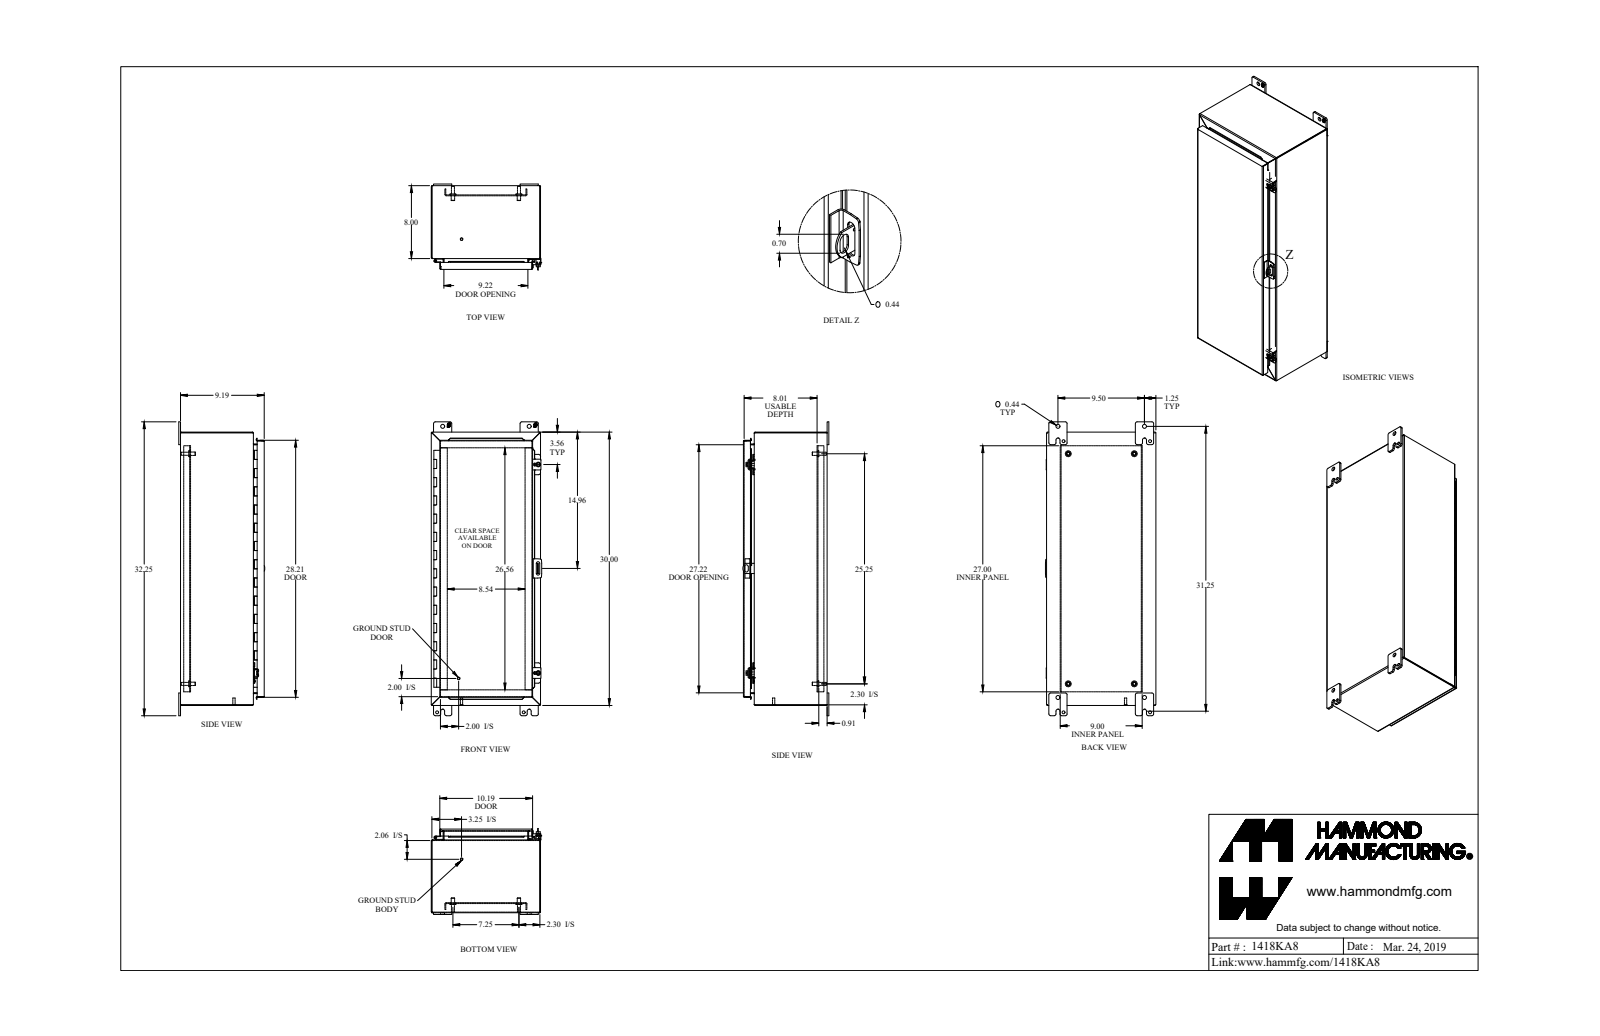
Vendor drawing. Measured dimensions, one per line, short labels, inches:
name: 1418KA8_Default
written by: SolidWorks 2019 (CONFIG_CONTROL_DESIGN)
unit: in
bodies: 38 solids, 1209 faces (739 planar, 402 cylindrical, 68 other)
size: 32.25 × 12.125 × 9.437
volume: 159.3 in³; area: 4 151 in²
holes: 4× ⌀0.313, 4× ⌀0.437, 4× ⌀0.5, 2× ⌀0.213, 2× ⌀0.265, 2× ⌀0.307, 2× ⌀0.375, 2× ⌀0.445, 1× ⌀0.125, 1× ⌀0.187
bosses: 4× ⌀0.65, 4× ⌀0.375, 4× ⌀0.33, 2× ⌀1, 2× ⌀0.5, 2× ⌀0.39, 2× ⌀0.281, 2× ⌀0.25
rounds: 26× R0.188, 24× R0.036, 24× R0.108, 13× R0.048, 13× R0.143, 8× R0.045, 8× R0.218, 8× R0.25
face distances: 0.072, 9.113, 11.928, 9.041, 0.937, 9.185, 0.095, 1.009, 8.081, 8.009
hole spacings: 1.736, 9.5, 29.75, 31.23, 7.25, 2.434, 3.204, 8.896
